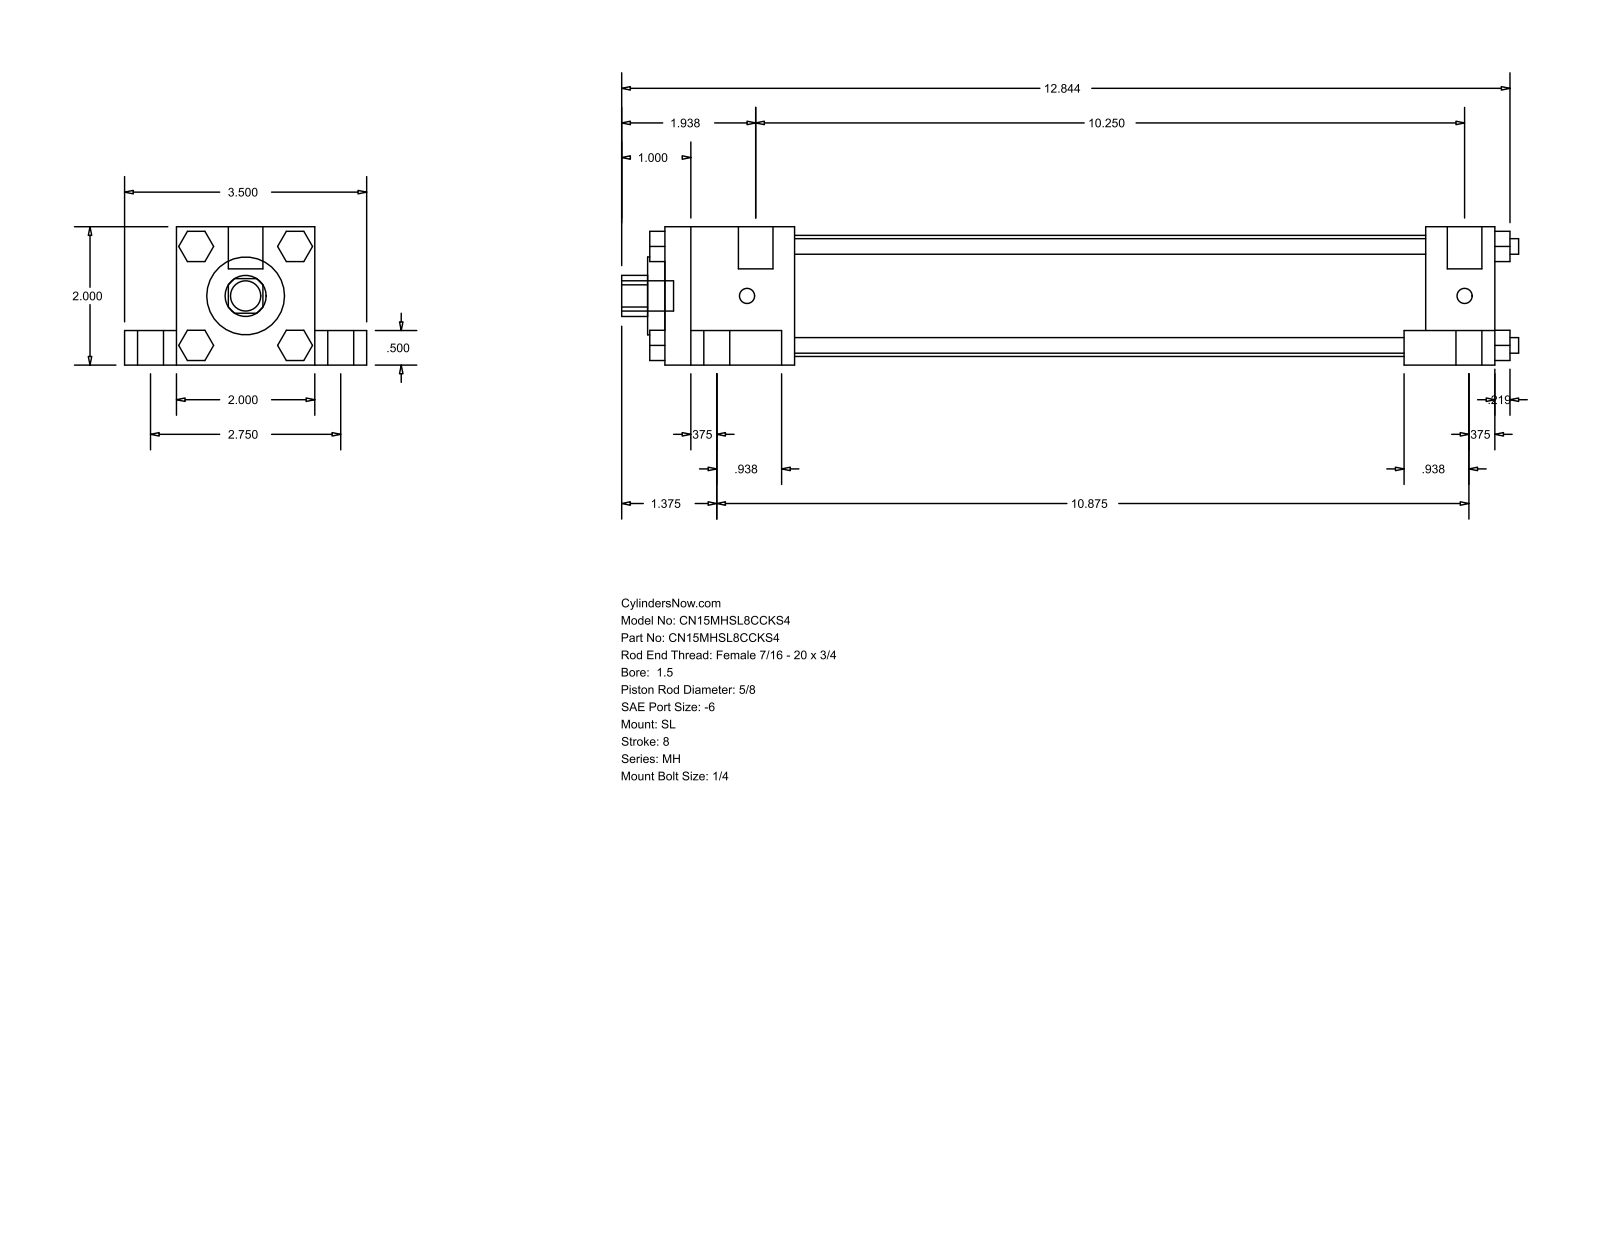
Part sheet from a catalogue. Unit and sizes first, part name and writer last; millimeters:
Units: millimetres
Overall size (bounding box): 329.41 × 88.9 × 50.8
Round holes (diameter × count): ⌀15.88 ×1, ⌀28.57 ×1, ⌀44.45 ×1
Round bosses / shafts (diameter × count): ⌀15.88 ×4, ⌀9.53 ×4, ⌀5.71 ×4, ⌀5.56 ×4, ⌀12.7 ×2, ⌀11.11 ×1
Partial cylindrical surfaces — rounded edges, fillets, slot ends (radius × count): R7.54 ×1
Main face-to-face distances: 50.8, 38.1, 19.05, 12.7, 69.85, 304.8, 9.52, 33.34, 261.94, 279.39
Bodies: 0 solids, 148 faces (112 planar, 36 cylindrical, 0 other)
Part name (STEP PRODUCT): MH_SL__0150_0.625
STEP written by: GSSL Pune (CONFIG_CONTROL_DESIGN)
